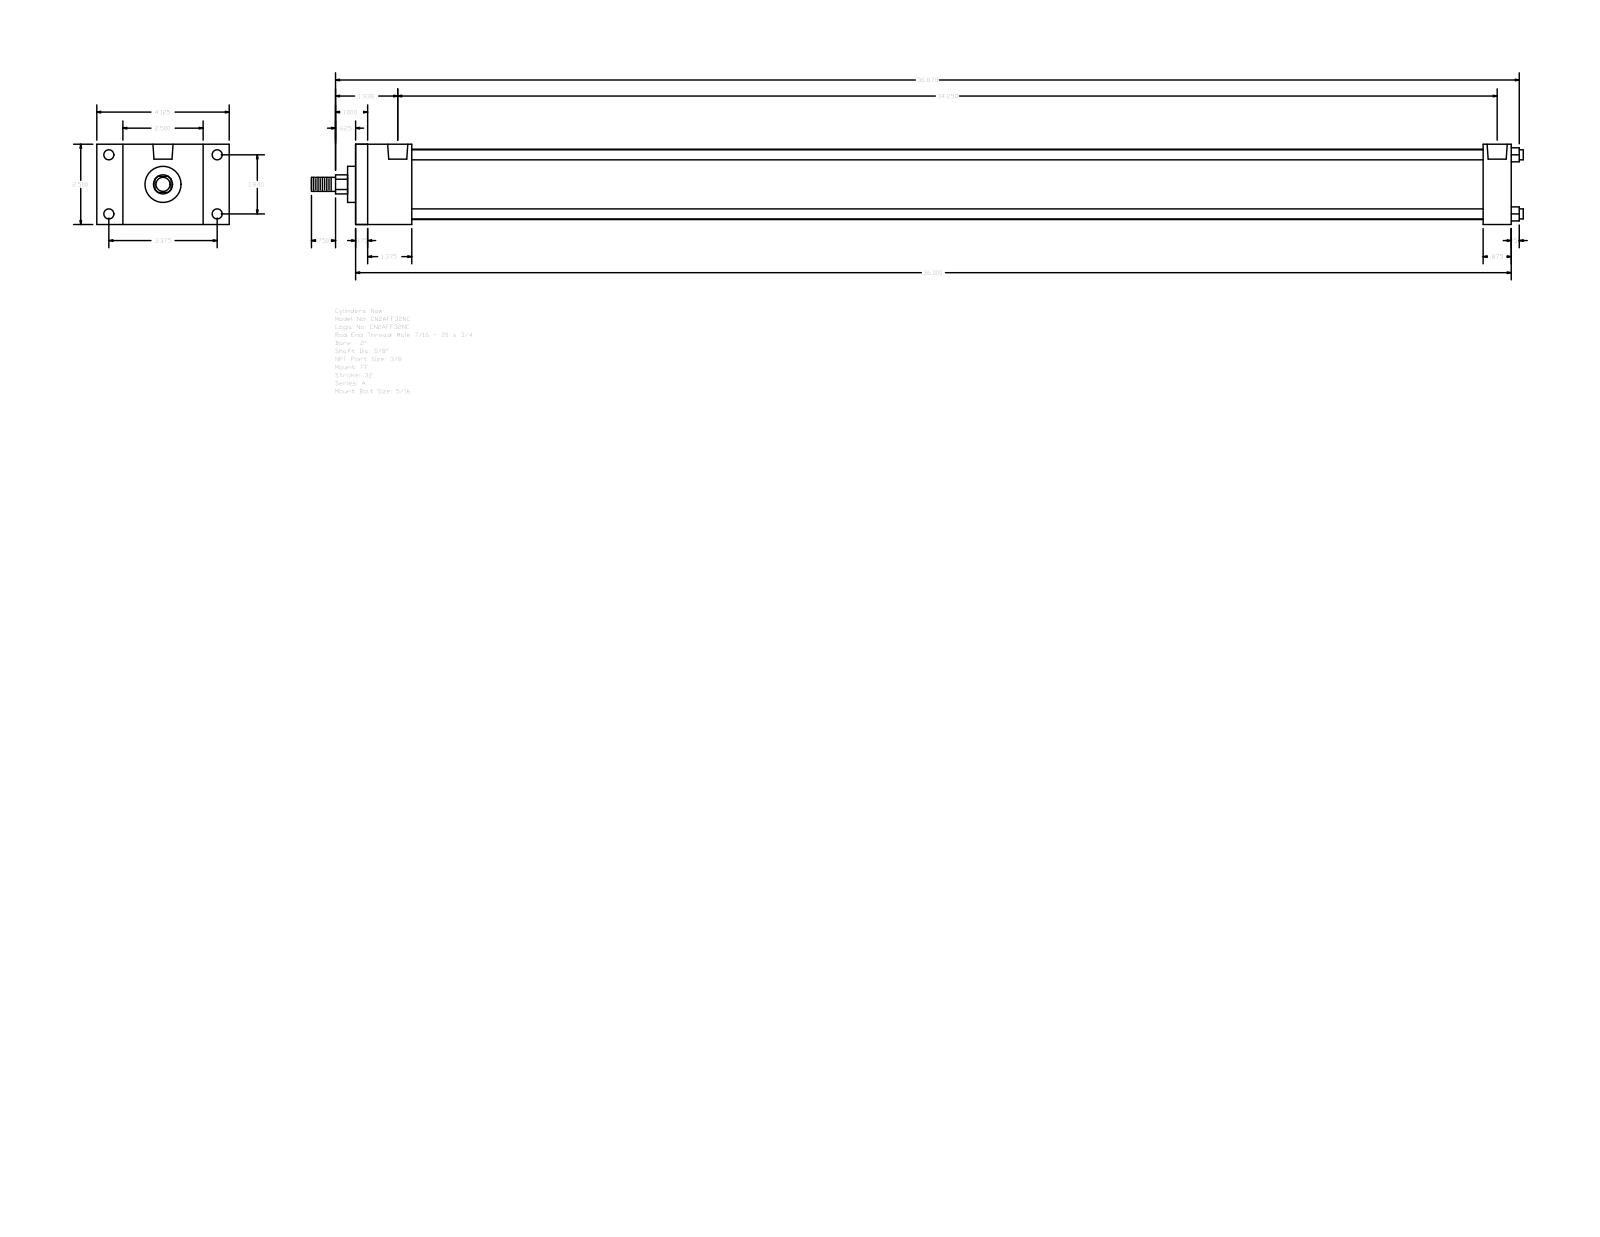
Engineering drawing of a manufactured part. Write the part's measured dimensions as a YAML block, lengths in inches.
part_name: "A_FF__0200_0.625"
step_written_by: "GSSL Pune (CONFIG_CONTROL_DESIGN)"
units: inches
bodies: {solids: 0, faces: 92, planar: 64, cylindrical: 28, other: 0}
overall_size: [37.75, 4.125, 2.5]
round_holes:
  - {diameter: 0.219, count: 4}
  - {diameter: 0.313, count: 4}
  - {diameter: 0.627, count: 2}
round_bosses_or_shafts:
  - {diameter: 0.313, count: 4}
  - {diameter: 2.19, count: 1}
  - {diameter: 1.125, count: 1}
  - {diameter: 0.625, count: 1}
  - {diameter: 0.437, count: 1}
partial_cylinders:
  - {radius: 0.297, count: 1}
face_to_face_distances: [2.5, 36, 0.375, 35.625, 1.375, 1.75, 35.125, 34.75, 33.375, 34.25]
hole_center_spacings: [1.84, 3.375, 3.844, 33.937, 0.156, 0.157, 34.093, 34.094]
